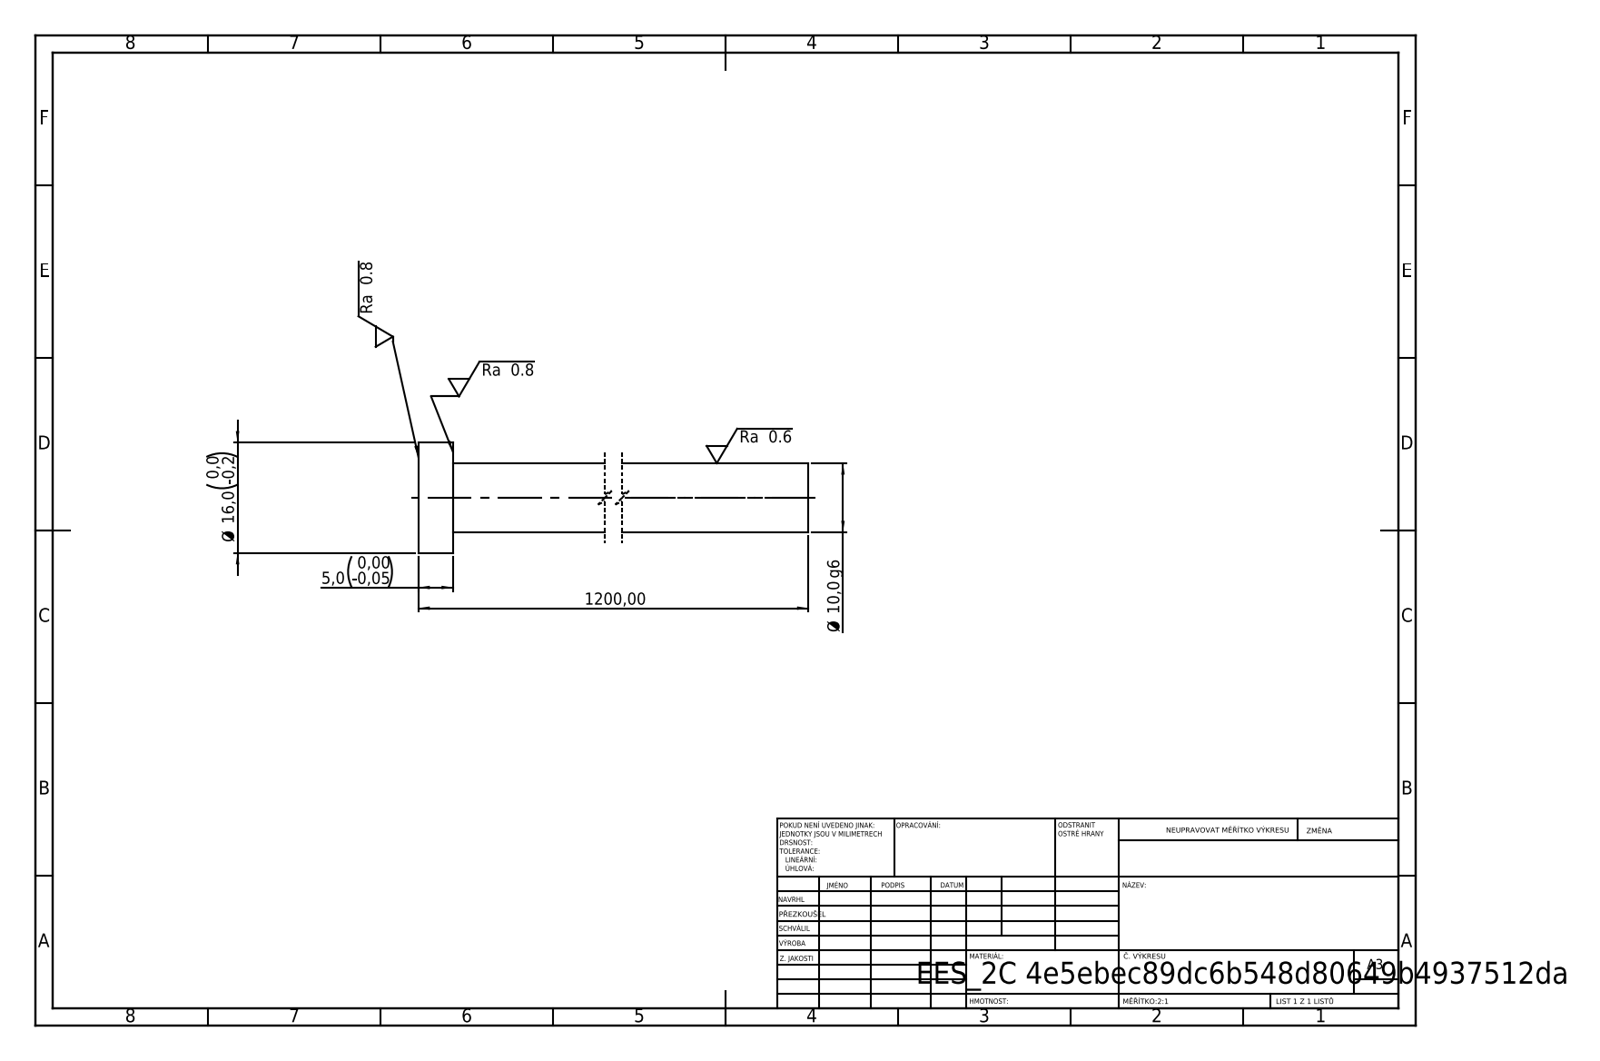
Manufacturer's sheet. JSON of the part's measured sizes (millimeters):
{"step_written_by": "SolidWorks 2019 (CONFIG_CONTROL_DESIGN)", "units": "millimeters", "bodies": {"solids": 1, "faces": 7, "planar": 3, "cylindrical": 4, "other": 0}, "overall_size": [1200, 16, 16], "volume_mm3": 94860, "surface_area_mm2": 38195, "round_bosses_or_shafts": [[16, 1], [10, 1]], "face_to_face_distances": [5, 1200, 1195]}
